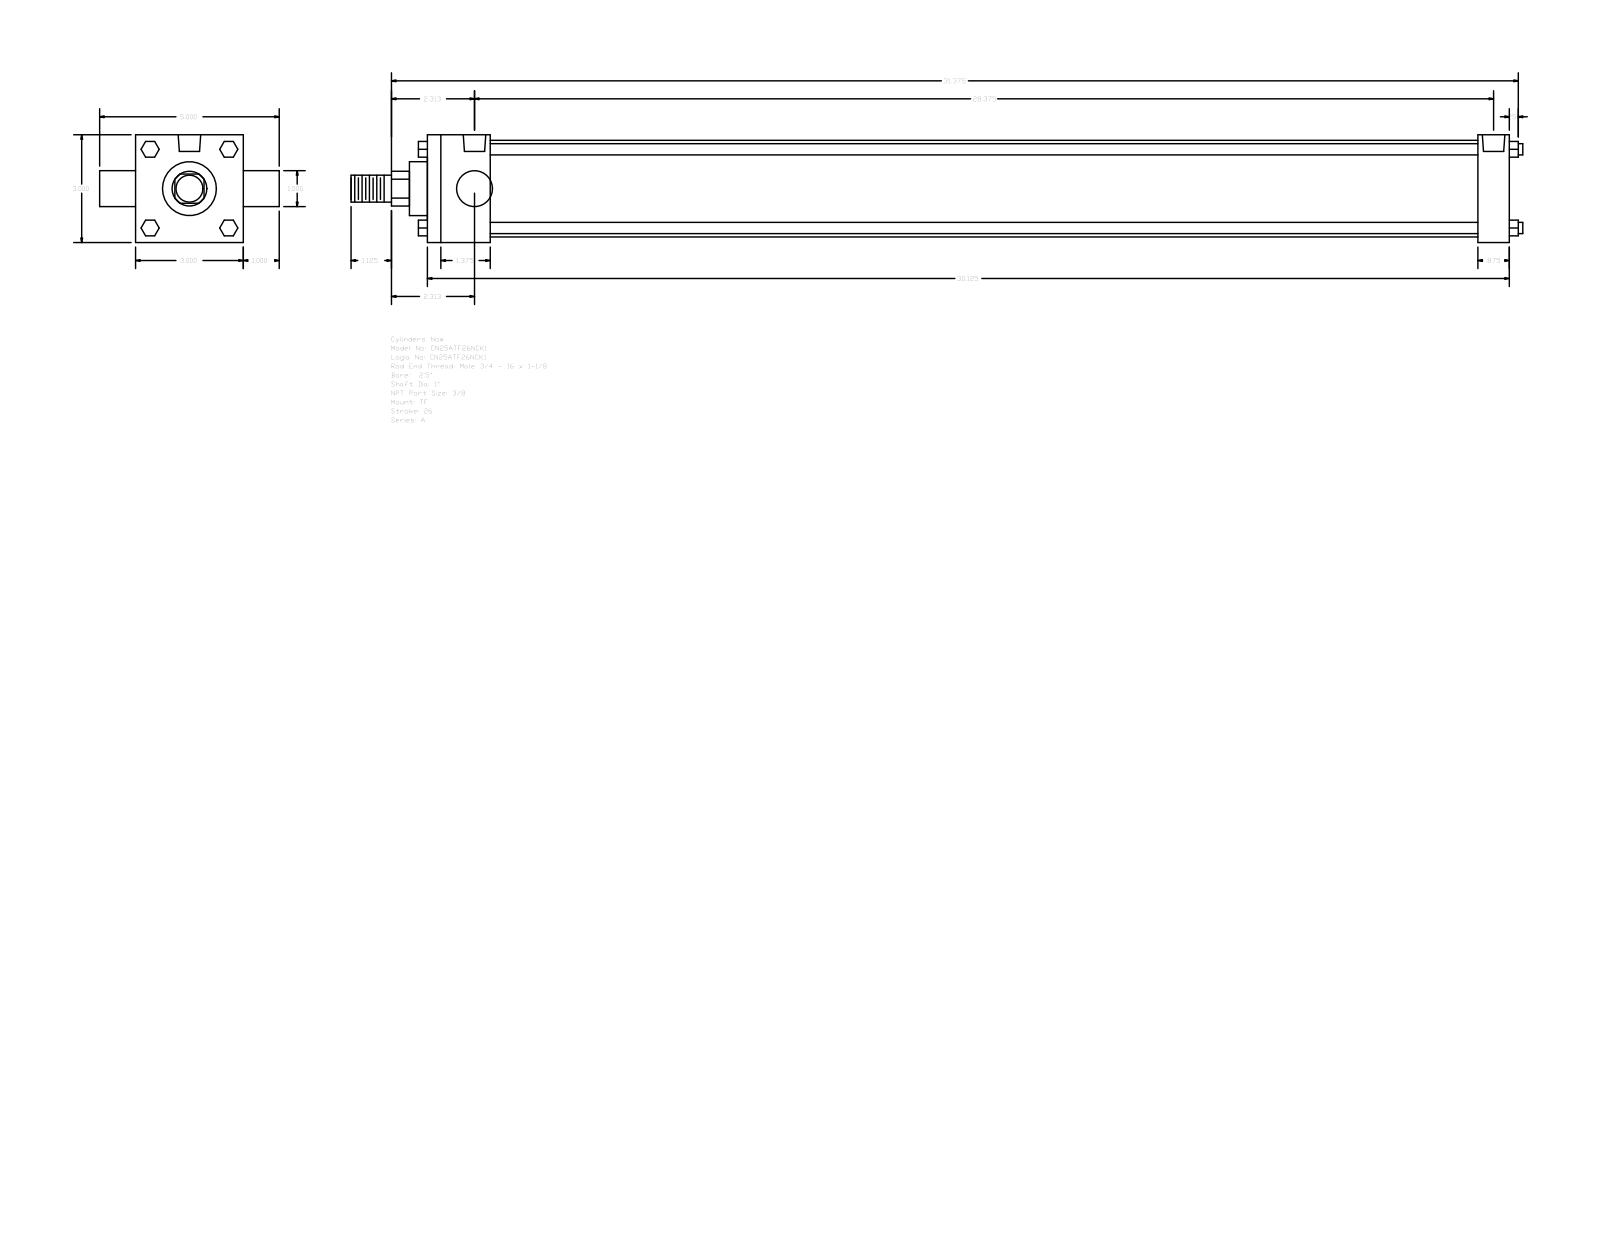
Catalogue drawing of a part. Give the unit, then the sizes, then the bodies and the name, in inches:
Units: inches
Overall size (bounding box): 32.625 × 5 × 3
Round holes (diameter × count): ⌀0.219 ×3, ⌀0.627 ×2
Round bosses / shafts (diameter × count): ⌀0.313 ×4, ⌀1 ×2, ⌀2.69 ×1, ⌀1.5 ×1, ⌀0.75 ×1
Partial cylindrical surfaces — rounded edges, fillets, slot ends (radius × count): R0.484 ×1
Main face-to-face distances: 3, 30.125, 1.75, 29.25, 27.5, 28.375, 0.875, 1, 4, 0.5
Hole centre spacings: 0.094, 28.469, 28.375, 28.562
Bodies: 0 solids, 120 faces (92 planar, 28 cylindrical, 0 other)
Part name (STEP PRODUCT): A_TF__0250_1
STEP written by: GSSL Pune (CONFIG_CONTROL_DESIGN)
